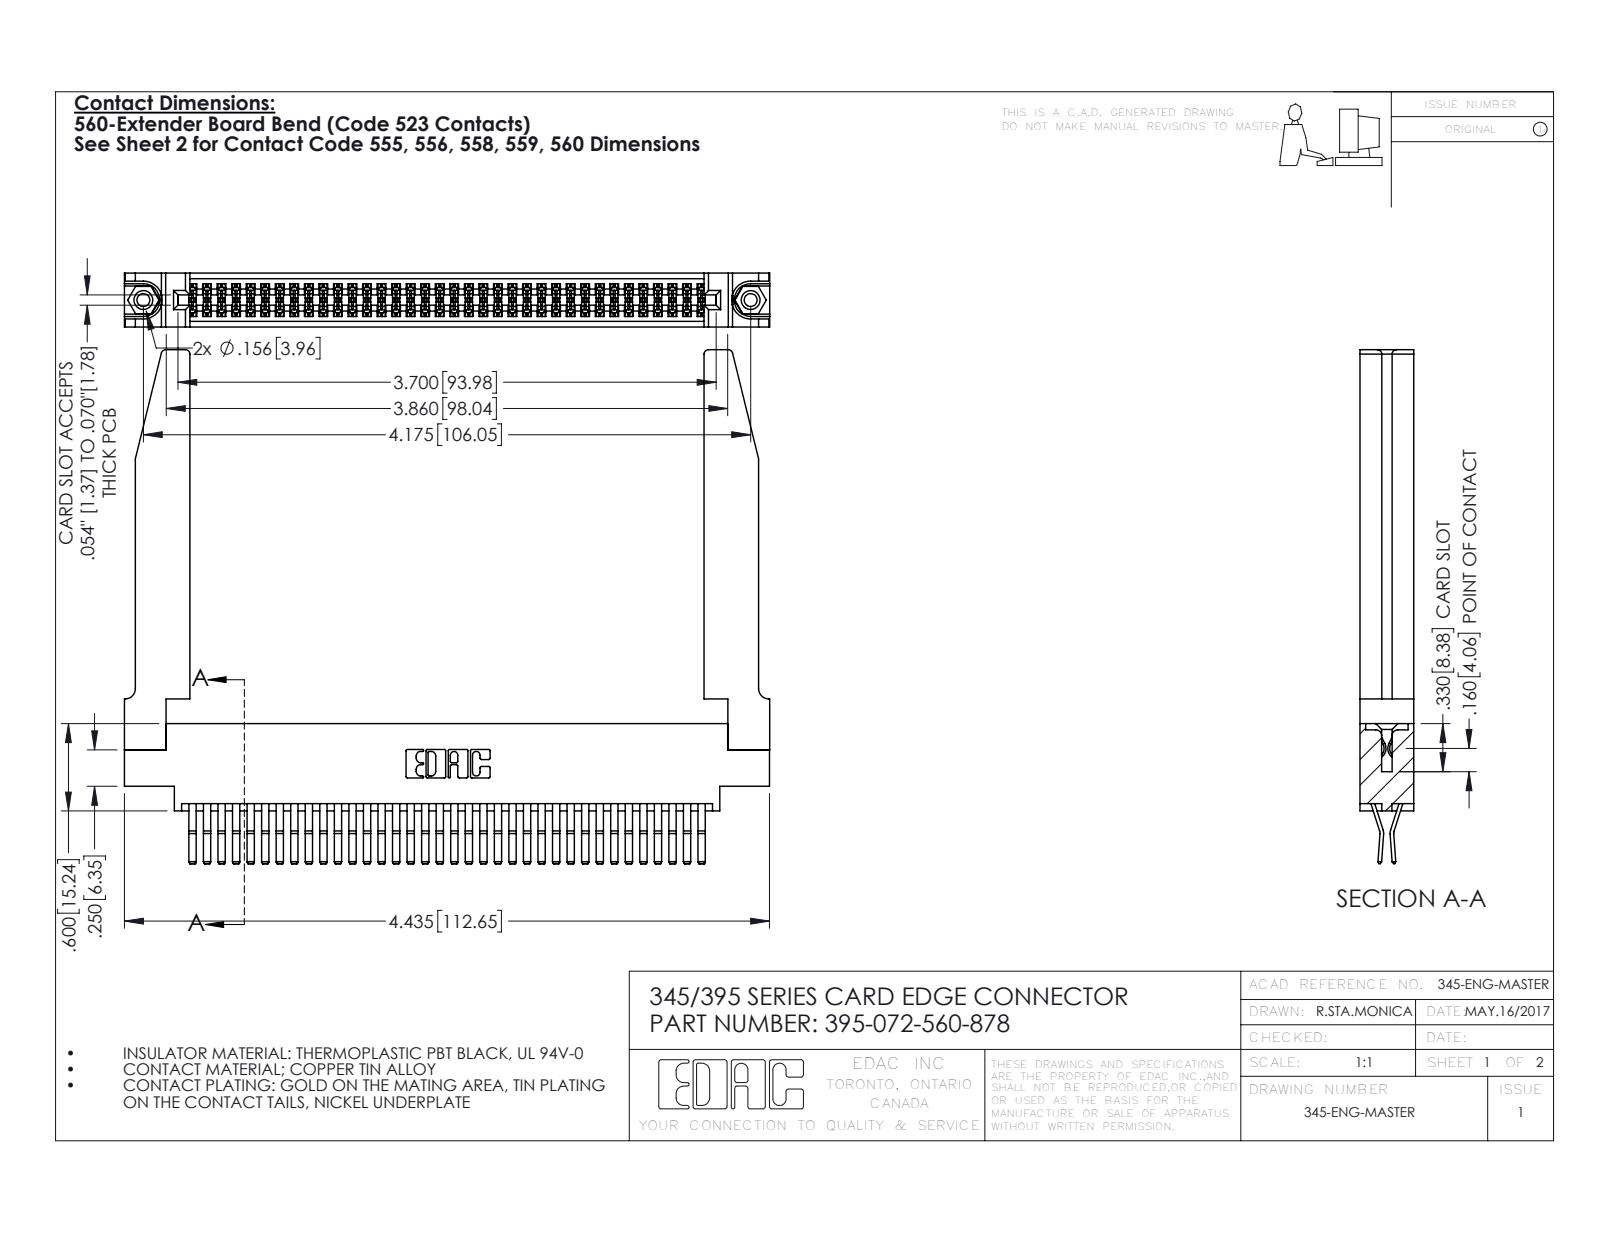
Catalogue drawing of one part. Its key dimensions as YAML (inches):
part_name: "345 Part_0.170 Offset - 0.156 Dia-TH; 345-292-001_560 Tail; 345-250-001_345-250-001-102; 395-072-560-878 (+1 more)"
step_written_by: "SolidWorks 2016 (CONFIG_CONTROL_DESIGN)"
units: inches
bodies: {solids: 77, faces: 4108, planar: 2602, cylindrical: 1454, other: 52}
overall_size: [4.436, 3.532, 0.37]
volume: 1.161
surface_area: 38.29
round_holes:
  - {diameter: 0.089, count: 2}
  - {diameter: 0.125, count: 2}
  - {diameter: 0.156, count: 2}
  - {diameter: 0.064, count: 1}
round_bosses_or_shafts:
  - {diameter: 0.155, count: 2}
partial_cylinders:
  - {radius: 0.006, count: 109}
  - {radius: 0.01, count: 22}
  - {radius: 0.03, count: 8}
  - {radius: 0.007, count: 6}
  - {radius: 0.031, count: 6}
  - {radius: 0.026, count: 3}
  - {radius: 0.01, count: 2}
  - {radius: 0.014, count: 2}
face_to_face_distances: [0.37, 0.072, 0.298, 0.025, 0.2, 0.098, 0.272, 0.225, 0.175, 0.148]
hole_center_spacings: [0.27, 3.939, 4.175]
